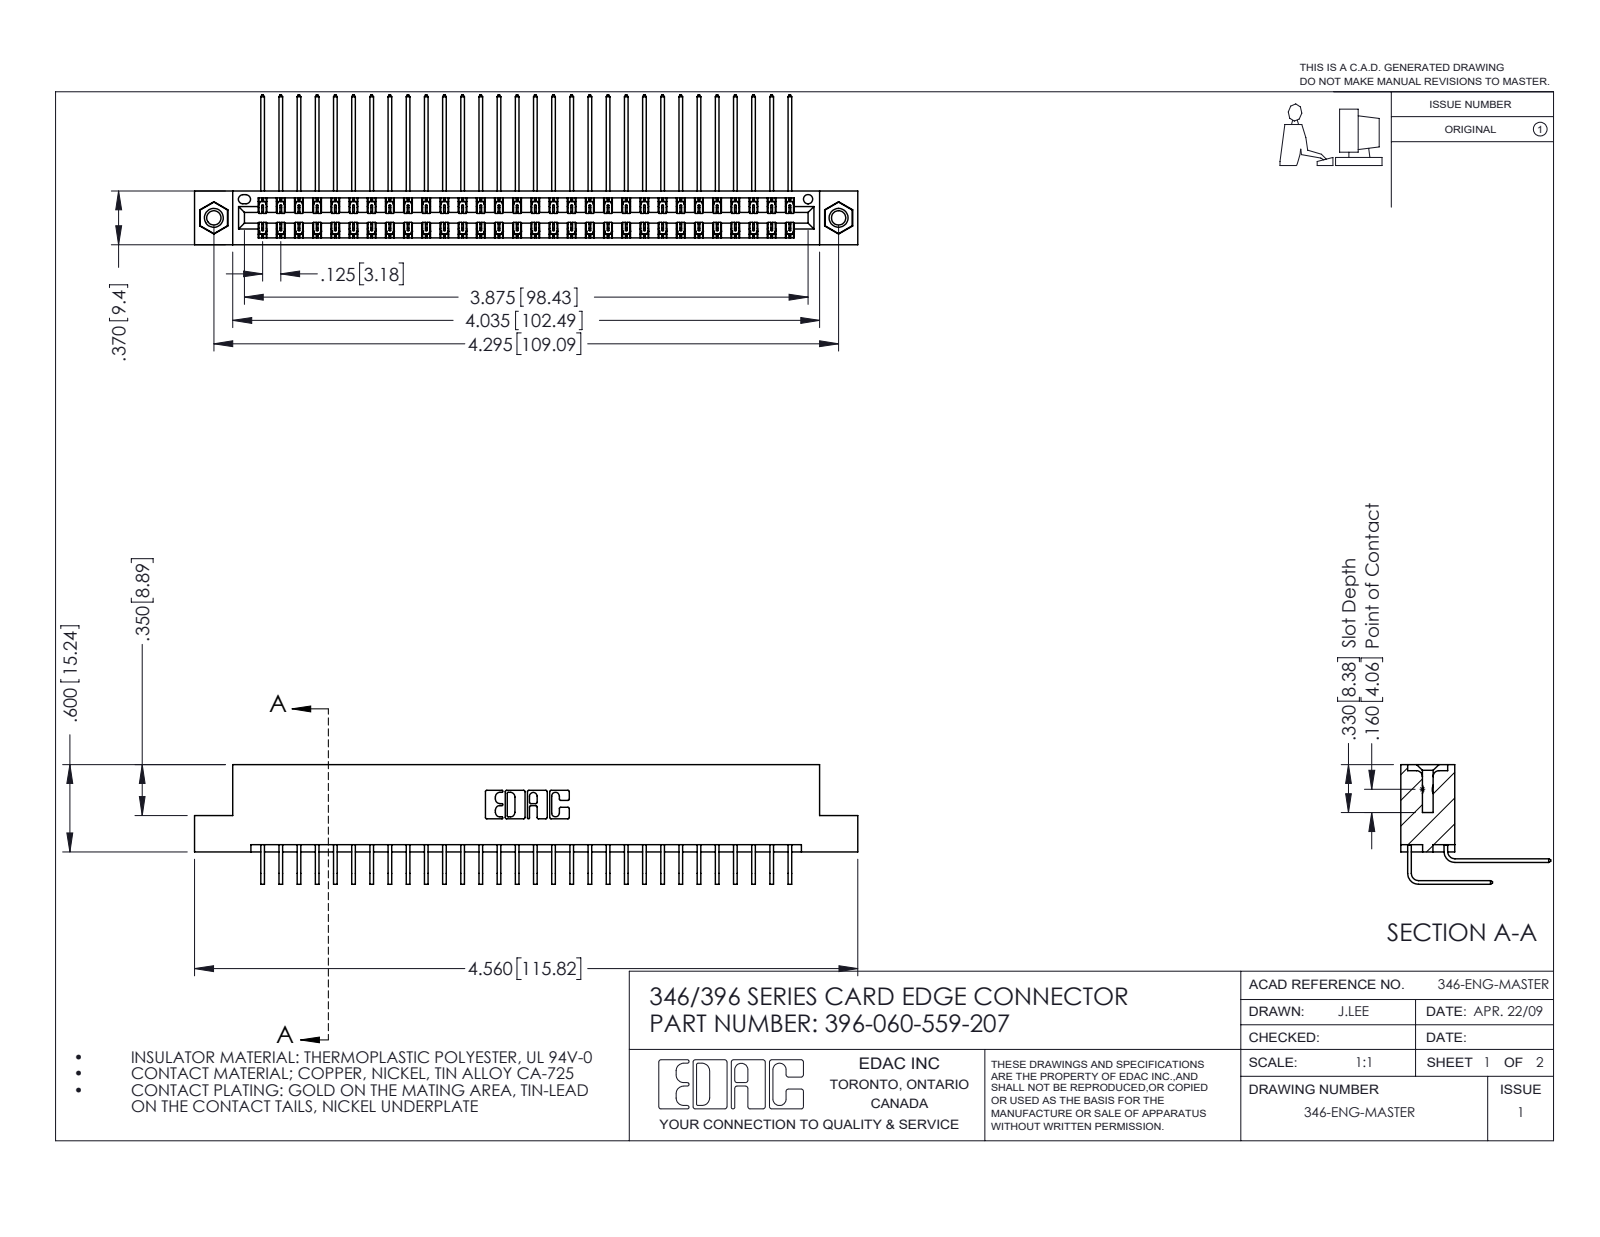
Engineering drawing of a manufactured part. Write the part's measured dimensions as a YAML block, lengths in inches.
part_name: "396-060-559-207; 345-250-001_345-250-005-103; 345-292-001_559 Tail - 2; 346 Part_Flush Mounting Lugs - 0.156 Dia-TI (+1 more)"
step_written_by: "SolidWorks 2016 (CONFIG_CONTROL_DESIGN)"
units: inches
bodies: {solids: 63, faces: 3422, planar: 2328, cylindrical: 1078, other: 16}
overall_size: [4.56, 1.03, 0.823]
volume: 0.704
surface_area: 26.91
round_holes:
  - {diameter: 0.098, count: 2}
  - {diameter: 0.125, count: 2}
  - {diameter: 0.156, count: 2}
  - {diameter: 0.064, count: 1}
round_bosses_or_shafts:
  - {diameter: 0.155, count: 2}
partial_cylinders:
  - {radius: 0.006, count: 90}
  - {radius: 0.01, count: 22}
  - {radius: 0.007, count: 6}
  - {radius: 0.031, count: 6}
  - {radius: 0.026, count: 3}
  - {radius: 0.014, count: 2}
  - {radius: 0.022, count: 2}
  - {radius: 0.024, count: 2}
face_to_face_distances: [0.048, 0.322, 0.025, 0.25, 0.37, 0.072, 0.298, 0.275, 0.148, 0.222]
hole_center_spacings: [0.246, 4.087, 4.295]
